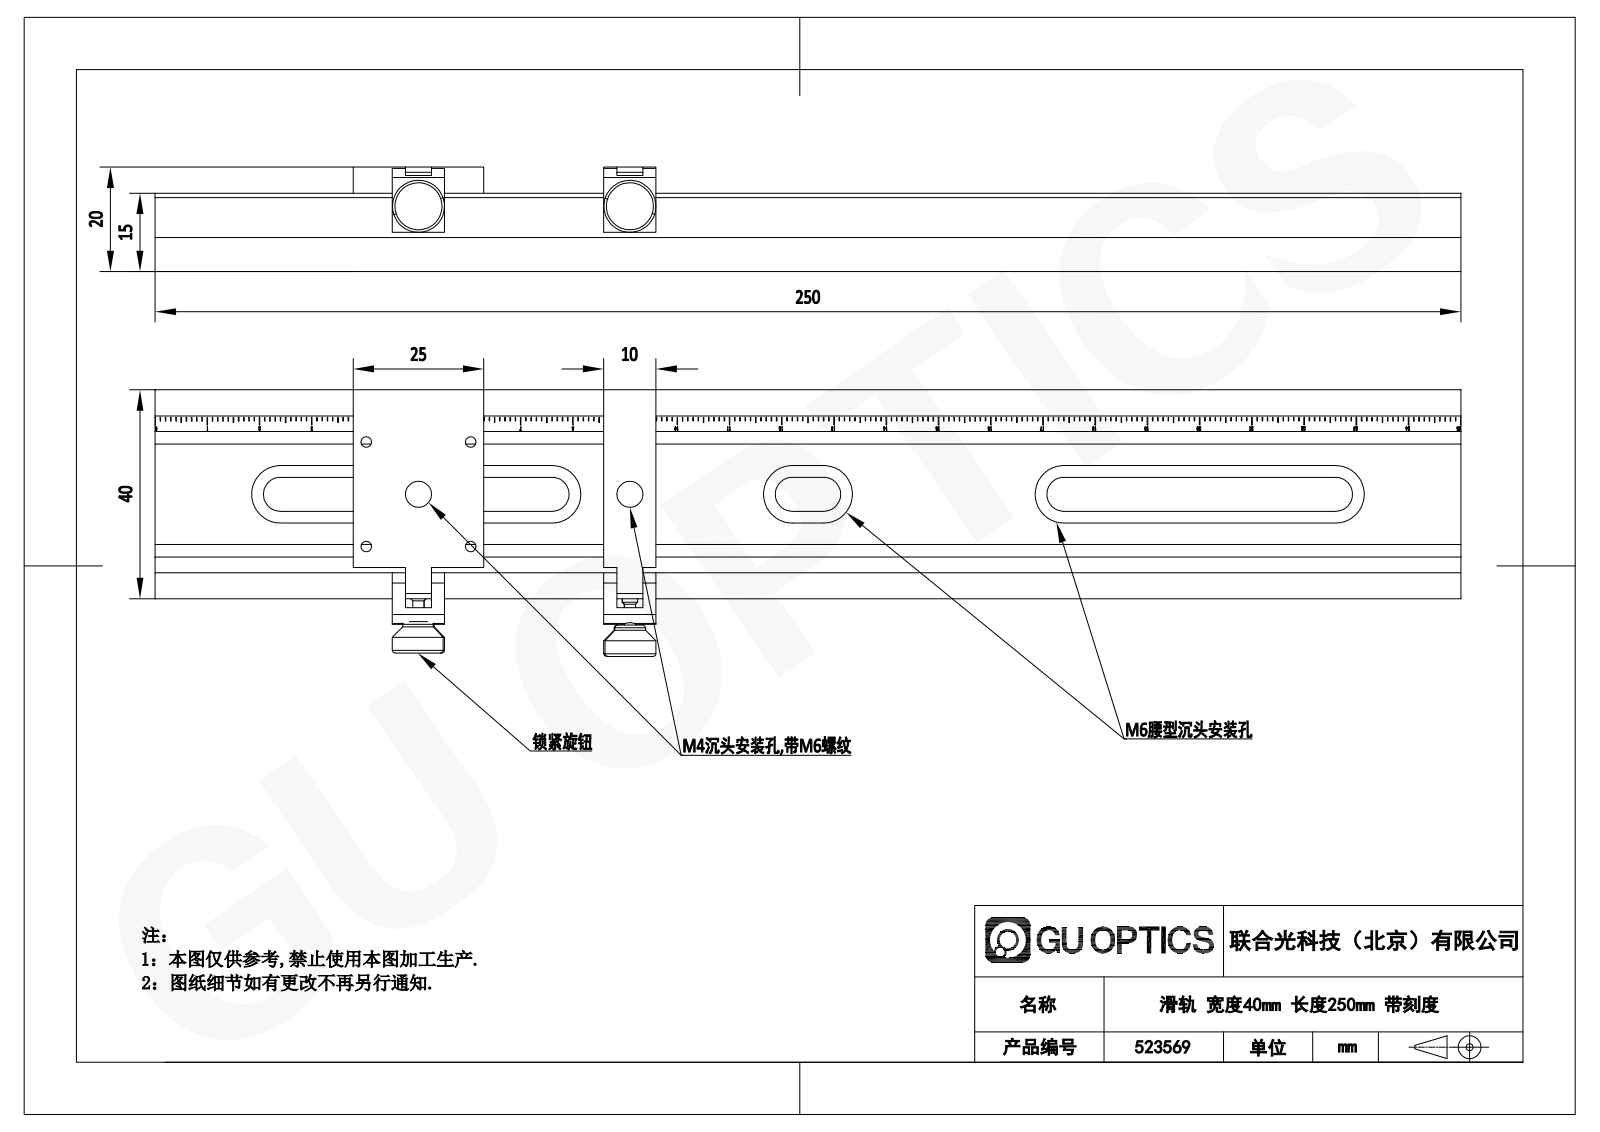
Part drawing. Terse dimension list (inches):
name: 523569
written by: SolidWorks 2020 (CONFIG_CONTROL_DESIGN)
unit: in
bodies: 8 solids, 2335 faces (1829 planar, 83 cylindrical, 423 other)
size: 9.843 × 2.009 × 0.787
volume: 5.828 in³; area: 62.91 in²
holes: 4× ⌀0.081, 2× ⌀0.098, 2× ⌀0.126, 2× ⌀0.197, 2× ⌀0.315, 1× ⌀0.059, 1× ⌀0.079
bosses: 2× ⌀0.394, 2× ⌀0.236, 2× ⌀0.118, 2× ⌀0.087
rounds: 6× R0.128, 6× R0.217, 1× R0.049, 1× R0.098, 1× R0.177, 1× R0.492
face distances: 0.571, 0.236, 0.02, 0.591, 0.256, 0.197, 0.335, 1.575, 0.315, 0.374
hole spacings: 0.557, 0.787, 1.113, 1.263, 1.594, 2.026
